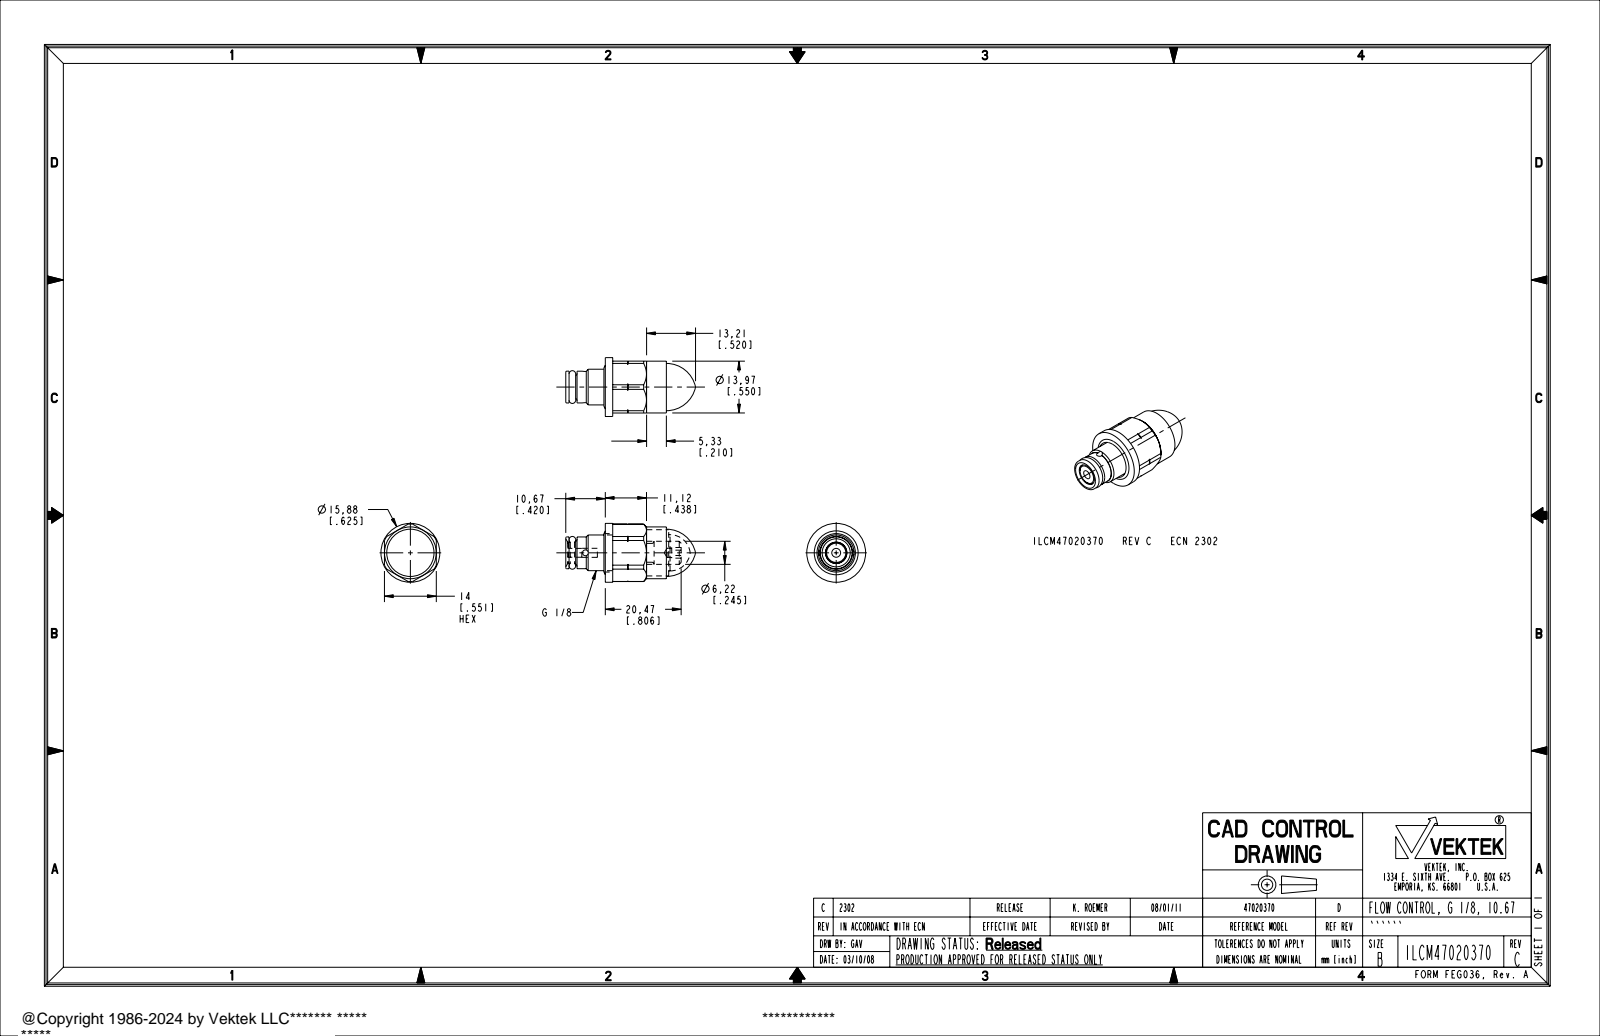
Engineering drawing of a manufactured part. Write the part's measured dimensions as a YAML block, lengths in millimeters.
part_name: "ILCM47020370"
step_written_by: "PRO/ENGINEER BY PARAMETRIC TECHNOLOGY CORPORATION, 2007460 (AUTOMOTIVE_DESIGN_CC2)"
units: millimeters
bodies: {solids: 3, faces: 125, planar: 41, cylindrical: 44, other: 40}
overall_size: [35.02, 15.88, 15.88]
volume: 3311
surface_area: 2801
round_holes:
  - {diameter: 1.57, count: 1}
  - {diameter: 2.39, count: 1}
  - {diameter: 2.44, count: 1}
  - {diameter: 2.49, count: 1}
  - {diameter: 5.79, count: 1}
  - {diameter: 9.8, count: 1}
  - {diameter: 10.37, count: 1}
round_bosses_or_shafts:
  - {diameter: 15.88, count: 1}
  - {diameter: 13.97, count: 1}
  - {diameter: 9.63, count: 1}
  - {diameter: 8.59, count: 1}
  - {diameter: 8.56, count: 1}
  - {diameter: 6.22, count: 1}
  - {diameter: 5.69, count: 1}
  - {diameter: 5.08, count: 1}
partial_cylinders:
  - {radius: 7.75, count: 1}
face_to_face_distances: [1.6, 12.4, 14, 10.8, 11.12, 11.14, 9.14, 9.12, 2, 20.92]
